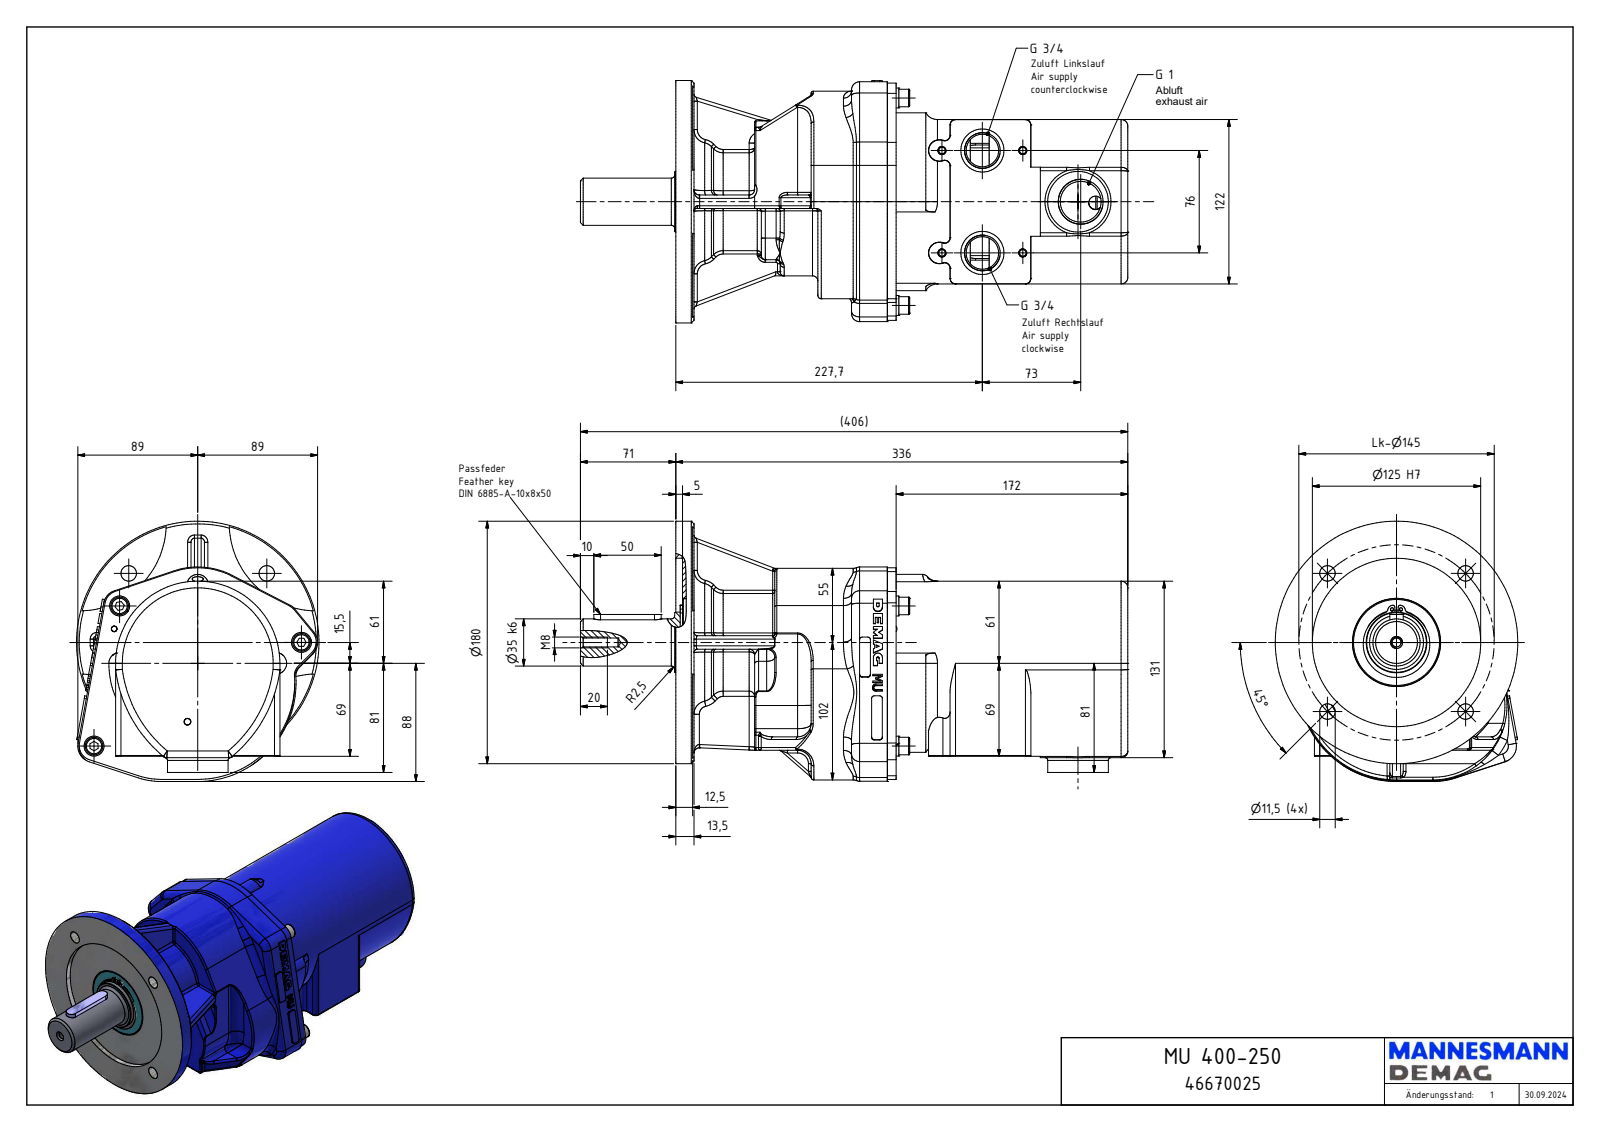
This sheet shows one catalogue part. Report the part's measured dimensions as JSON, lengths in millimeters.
{"part_name": "MU 400-250_46670025", "step_written_by": "Autodesk Inventor 2024 (AUTOMOTIVE_DESIGN)", "units": "millimeters", "bodies": {"solids": 2, "faces": 801, "planar": 282, "cylindrical": 264, "other": 255}, "overall_size": [406.45, 193.2, 180], "volume_mm3": 4661000, "surface_area_mm2": 268639, "round_holes": [[4.92, 4], [6.65, 4], [11.5, 4], [8.5, 3], [9.5, 3], [24.12, 2], [32, 2], [2.5, 1], [2.8, 1], [3.9, 1], [4.2, 1], [4.99, 1]], "round_bosses_or_shafts": [[14.8, 3], [13, 3], [8, 3], [45, 2], [180, 1], [65, 1], [42.5, 1], [35, 1]], "partial_cylinders_radius": [[2, 31], [2.5, 24], [4, 20], [6, 12], [1.5, 8], [3, 8], [11, 8], [1, 6]], "face_to_face_distances": [5, 335.65, 330.65, 1, 172, 158.65, 163.65, 322.15, 150.15, 8.5], "hole_center_spacings": [30, 81.71, 76, 57.36, 57.38, 60, 72.5, 72.51]}
